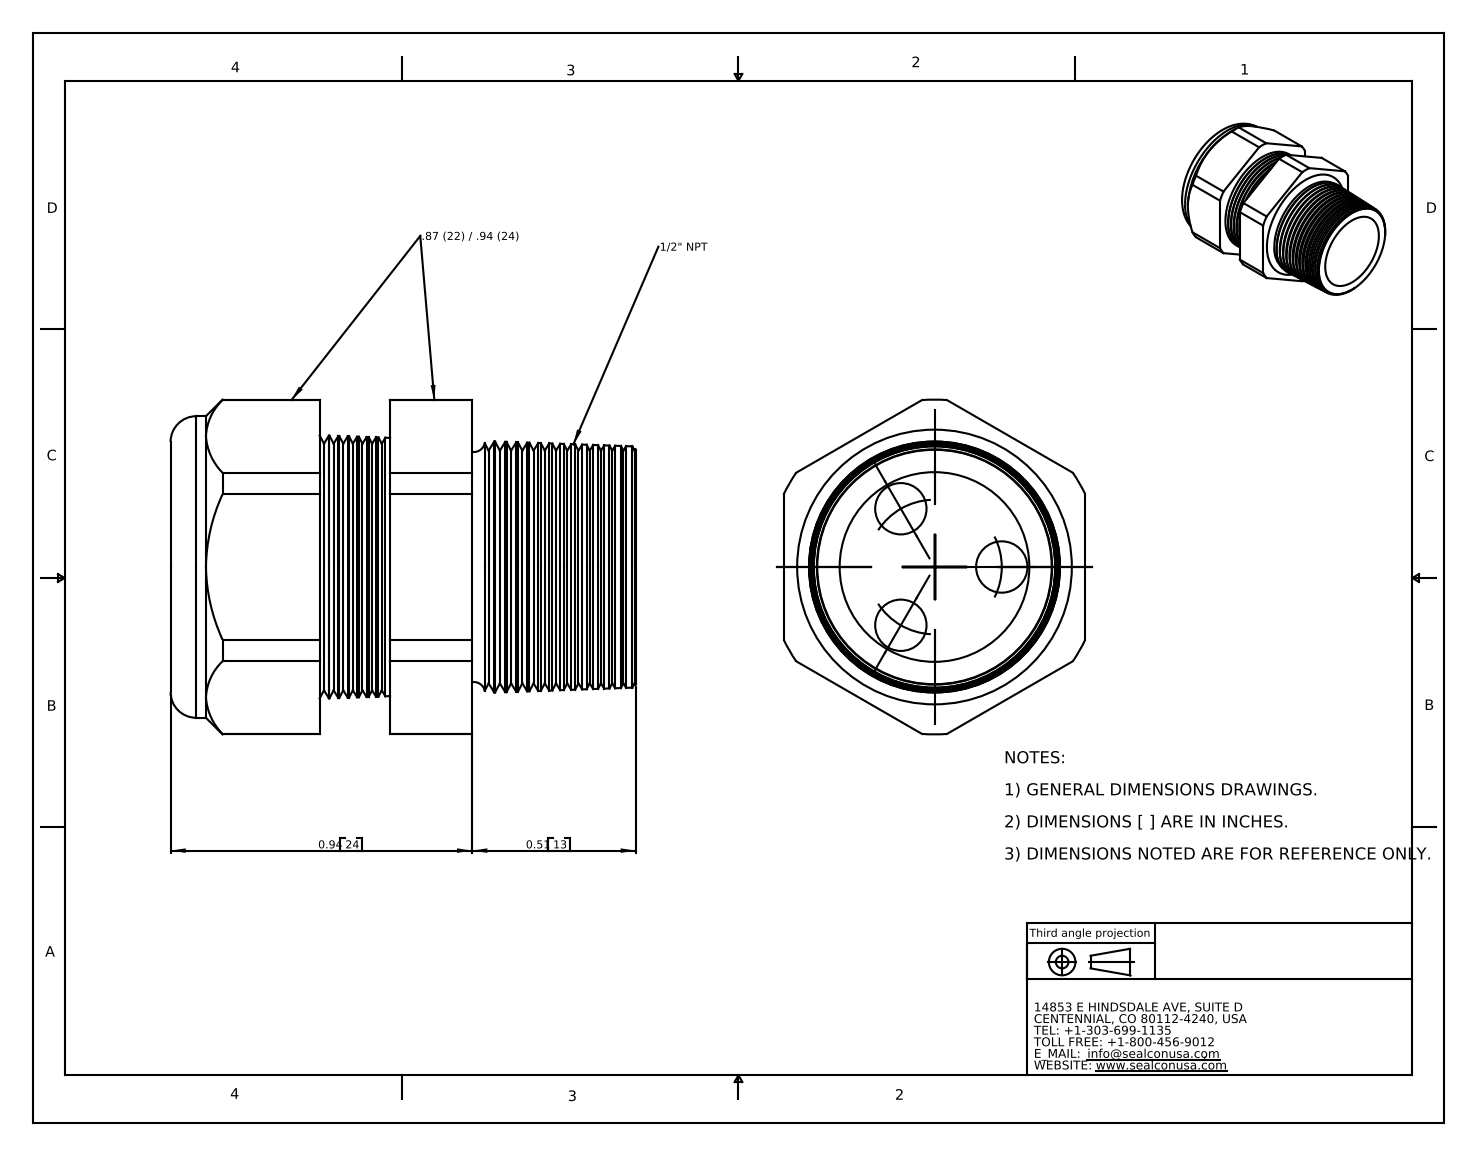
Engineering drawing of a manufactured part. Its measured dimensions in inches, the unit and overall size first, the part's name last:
Units: inches
Overall size (bounding box): 1.45 × 1.043 × 0.94
Round holes (diameter × count): ⌀0.16 ×3, ⌀0.58 ×1, ⌀0.6 ×1
Round bosses / shafts (diameter × count): ⌀0.94 ×1
Partial cylindrical surfaces — rounded edges, fillets, slot ends (radius × count): R0.522 ×1
Main face-to-face distances: 0.94, 0.22, 0.115, 0.334, 0.35, 0.465, 0.684, 0.02, 0.33, 0.444
Hole centre spacings: 0.363, 0.209, 0.21
Volume: 0.534 in³ · Surface area: 11.01 in²
Bodies: 2 solids, 186 faces (20 planar, 26 cylindrical, 140 other)
Part name (STEP PRODUCT): CD13N3-BR
STEP written by: SolidWorks 2007 (CONFIG_CONTROL_DESIGN)
